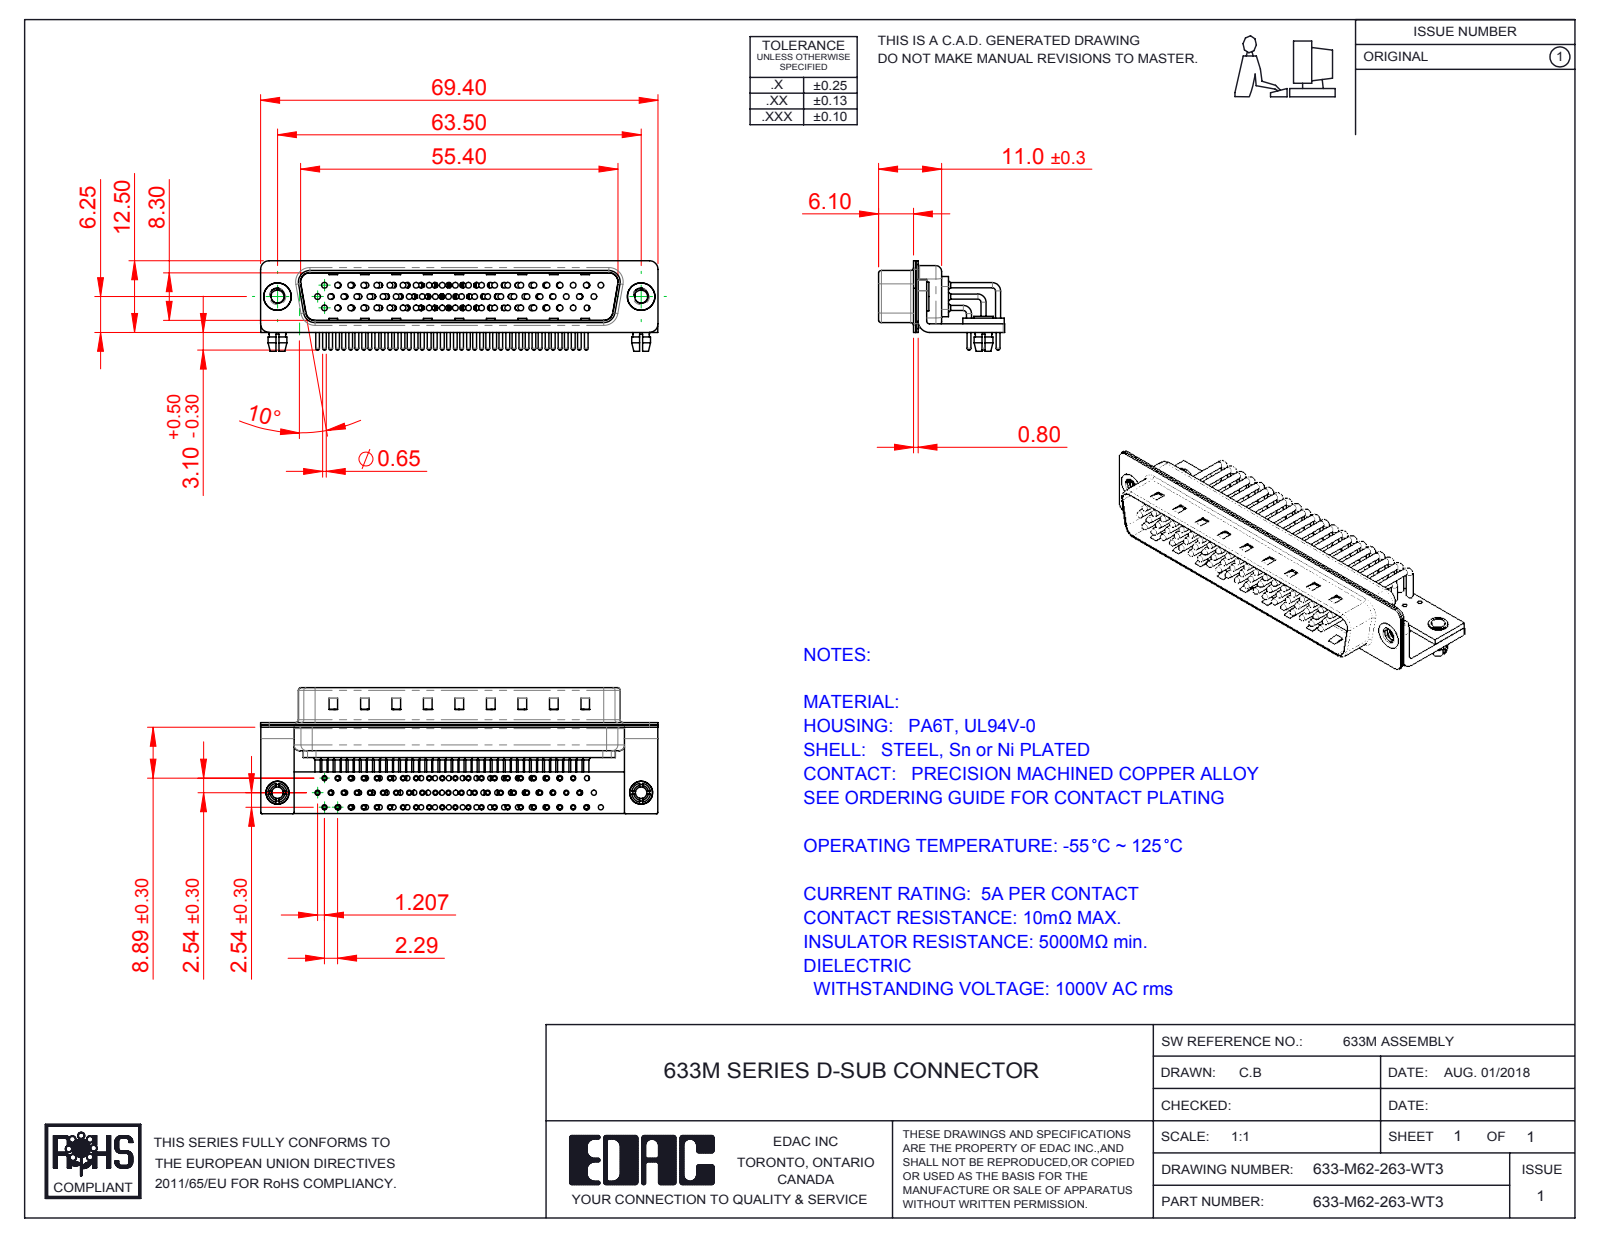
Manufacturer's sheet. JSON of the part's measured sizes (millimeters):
{"part_name": "633M Shell Front_62 Contacts; 633M Stabilizer Board_62 Contacts; 633M Contact Row 3; 633M Board Lock (+7 more)", "step_written_by": "SolidWorks 2016 (CONFIG_CONTROL_DESIGN)", "units": "millimeters", "bodies": {"solids": 72, "faces": 7498, "planar": 4245, "cylindrical": 2551, "other": 702}, "overall_size": [69.4, 22, 15.8], "volume_mm3": 5119, "surface_area_mm2": 15736, "round_holes": [[2, 64], [0.9, 62], [1, 62], [1.7, 62], [2.26, 2], [2.5, 2], [3.2, 2], [4, 2], [4.8, 2]], "round_bosses_or_shafts": [[0.9, 118], [1.5, 62], [0.65, 62], [1, 56], [5, 2], [4.9, 2], [4, 2], [3.4, 2]], "partial_cylinders_radius": [[1.01, 62], [0.25, 16], [1.5, 16], [2, 13], [0.5, 9], [1.6, 8], [0.6, 4], [0.65, 4]], "face_to_face_distances": [0.4, 0.85, 1.25, 1.5, 9.55, 1, 1.9, 10.4, 0.8, 8.3], "hole_center_spacings": [7.24, 2.41, 9.65, 4.83, 14.48, 16.89, 2.81, 2.32]}
